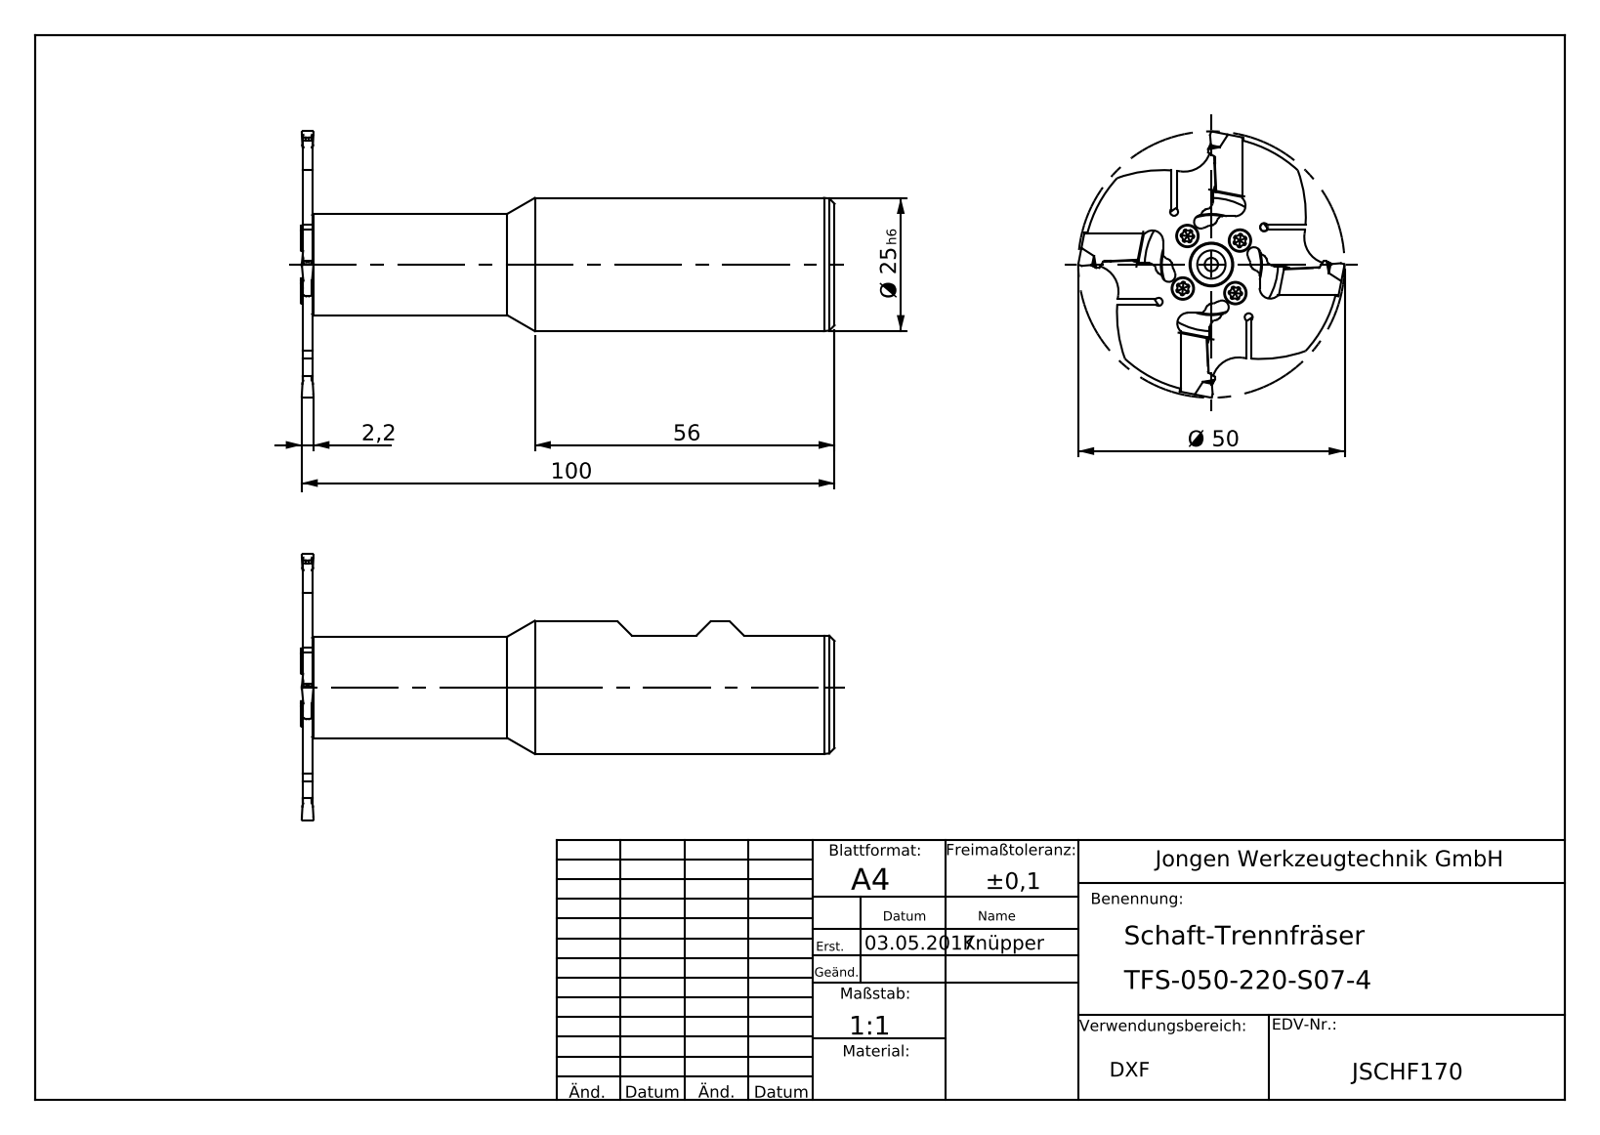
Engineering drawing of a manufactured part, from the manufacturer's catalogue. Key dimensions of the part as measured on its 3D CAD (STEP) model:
Part name (STEP PRODUCT): TFS-050-220-S07-4; JSCHF170 pk_Frserei (B); JSCHF170_1 pk
STEP written by: SolidWorks 2018 (AUTOMOTIVE_DESIGN)
Units: millimetres
Bodies: 2 solids, 134 faces (21 planar, 75 cylindrical, 38 other)
Overall size (bounding box): 100 × 51.97 × 51.97
Volume: 43 065 mm³ · Surface area: 12 660 mm²
Round holes (diameter × count): ⌀2.5 ×5, ⌀3.2 ×4, ⌀4.2 ×4, ⌀8 ×1, ⌀19.67 ×1
Round bosses / shafts (diameter × count): ⌀51.97 ×1, ⌀25 ×1, ⌀19 ×1
Partial cylindrical surfaces — rounded edges, fillets, slot ends (radius × count): R1 ×12, R1.25 ×4, R2 ×4, R4.64 ×4, R7.14 ×4
Main face-to-face distances: 2.2, 1.95, 97.8, 98.05, 100, 99.75, 1.7, 14.88, 11.31, 26.19
Hole centre spacings: 7, 9.9, 14
